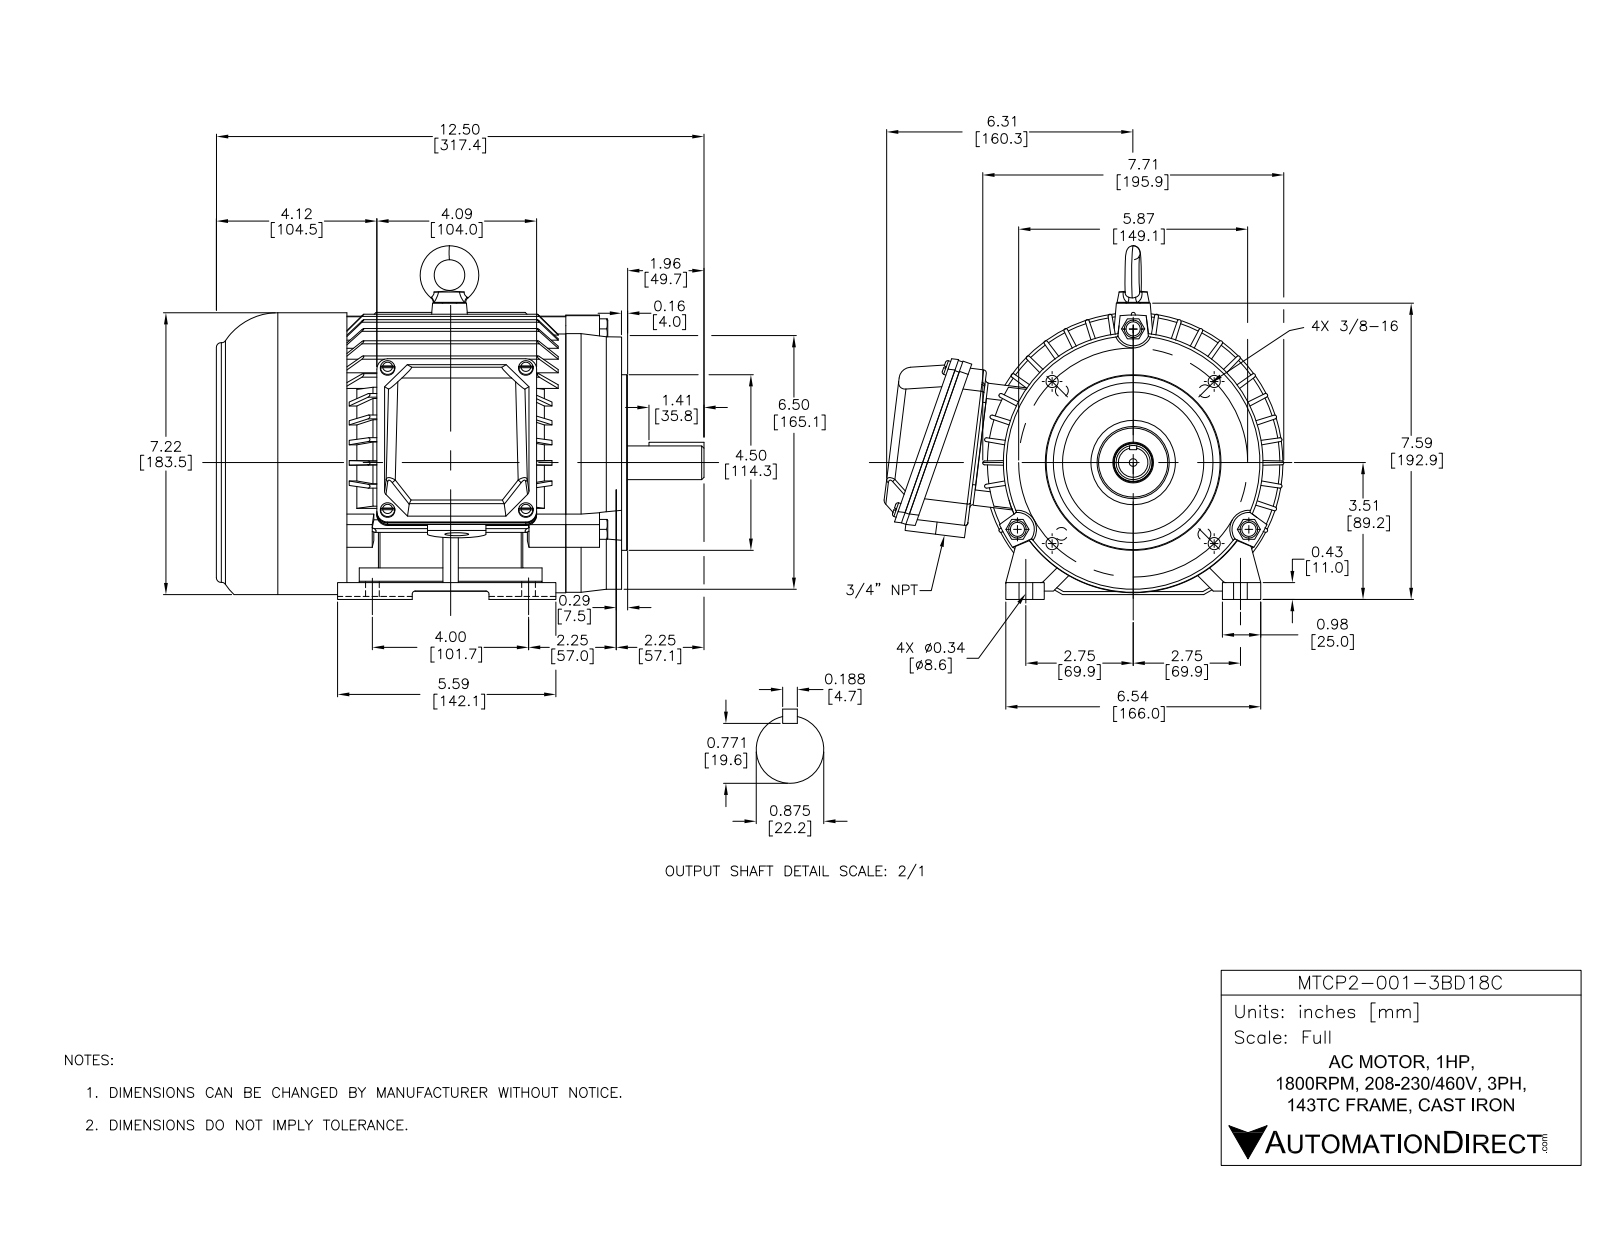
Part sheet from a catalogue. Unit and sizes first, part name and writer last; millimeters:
Units: millimetres
Overall size (bounding box): 317.5 × 260.2 × 230.3
Round holes (diameter × count): ⌀5.8 ×8, ⌀4.2 ×4, ⌀5 ×4, ⌀8 ×4, ⌀8.3 ×4, ⌀9 ×4, ⌀9.2 ×3, ⌀10 ×3, ⌀8 ×2, ⌀6.8 ×1, ⌀15.5 ×1, ⌀25.5 ×1
Round bosses / shafts (diameter × count): ⌀8 ×4, ⌀5 ×4, ⌀7.2 ×3, ⌀195 ×1, ⌀169 ×1, ⌀167 ×1, ⌀165 ×1, ⌀158 ×1
Partial cylindrical surfaces — rounded edges, fillets, slot ends (radius × count): R0.5 ×224, R1.3 ×26, R2 ×24, R7 ×16, R3 ×11, R6 ×4, R10 ×4, R5 ×2
Main face-to-face distances: 150, 4, 2, 224, 74, 225, 1, 149, 223, 76
Hole centre spacings: 90, 54, 98, 133.1, 4, 74.6, 87, 105.5
Volume: 4 778 000 mm³ · Surface area: 579 400 mm²
Bodies: 14 solids, 1419 faces (652 planar, 556 cylindrical, 211 other)
Part name (STEP PRODUCT): PEWWE-143TC
STEP written by: SolidWorks 2017 (AUTOMOTIVE_DESIGN)
